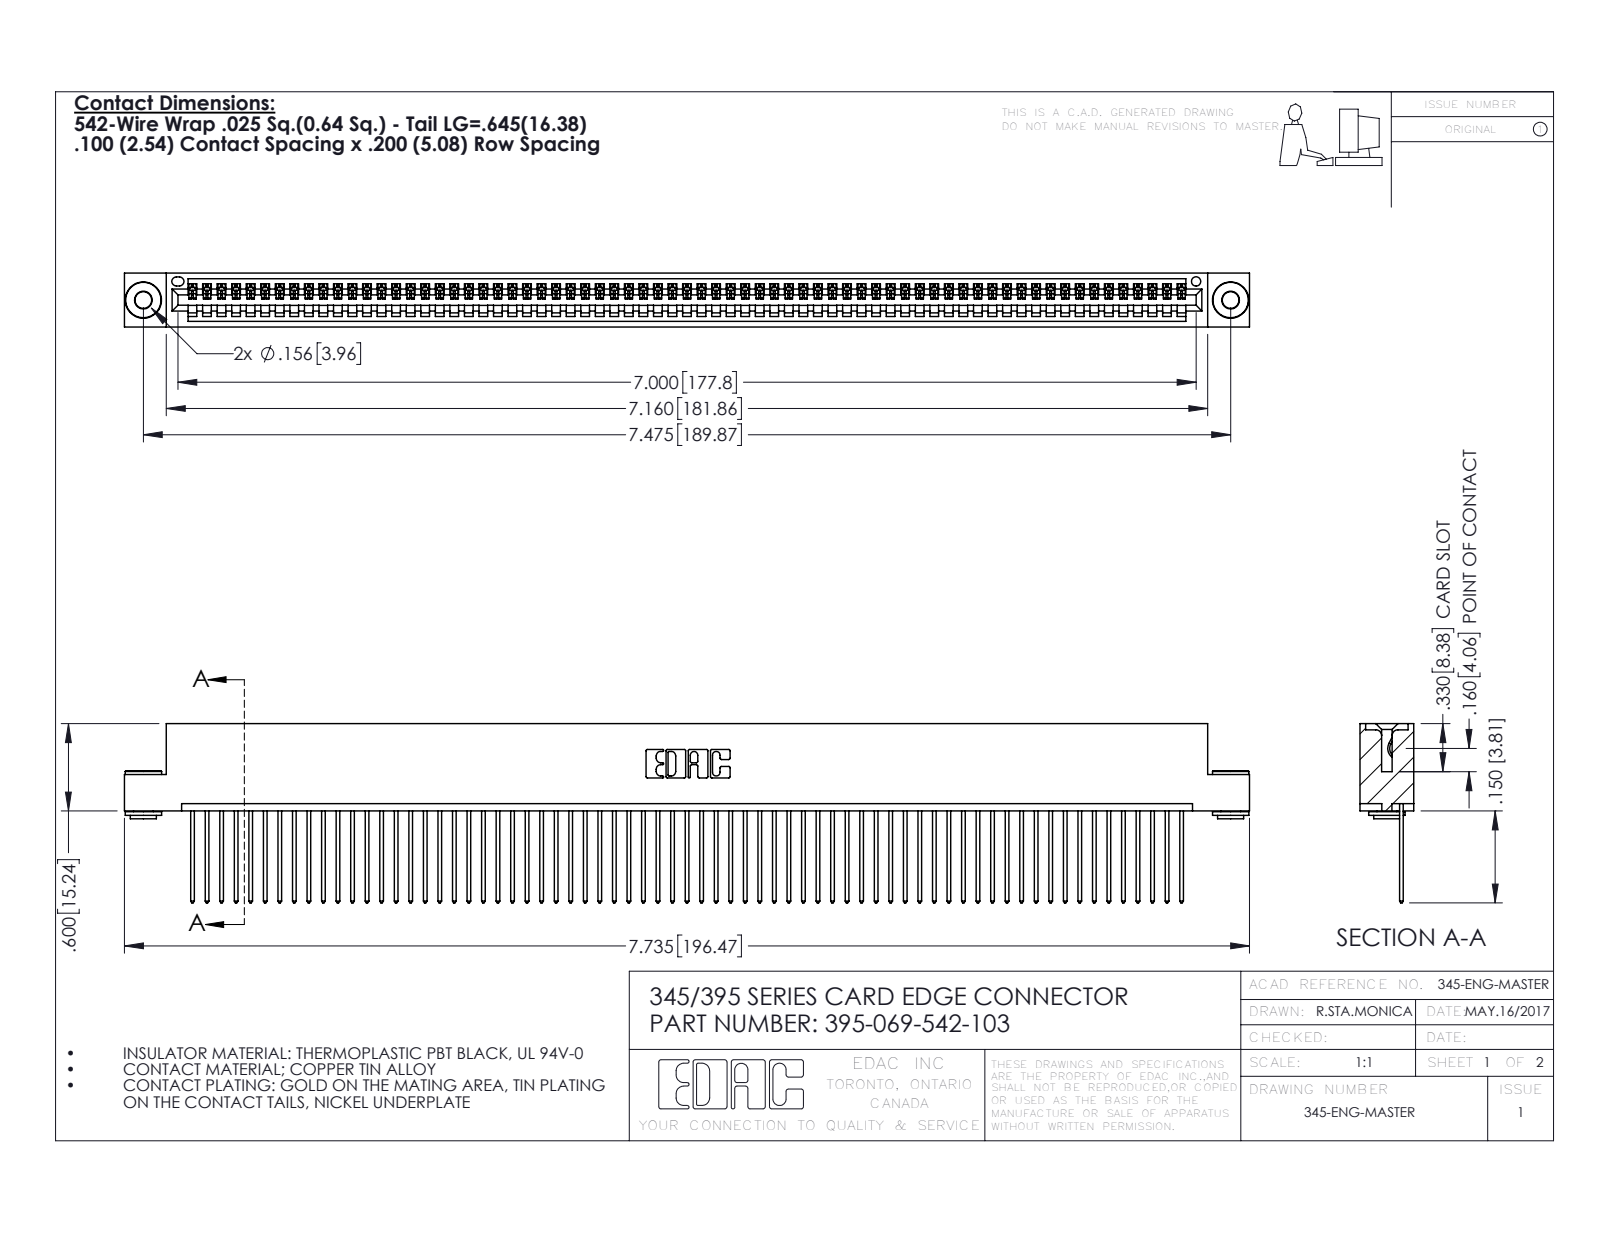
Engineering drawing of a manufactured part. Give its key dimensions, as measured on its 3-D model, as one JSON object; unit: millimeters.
{"part_name": "345 Part_Flush Mounting Lugs - 0.156 Dia-TH; 395-069-542-103; 345-250-002_345-250-002-102; 345-292-001_345-293-142", "step_written_by": "SolidWorks 2016 (CONFIG_CONTROL_DESIGN)", "units": "millimeters", "bodies": {"solids": 72, "faces": 4166, "planar": 2850, "cylindrical": 1308, "other": 8}, "overall_size": [196.5, 31.3, 9.4], "volume_mm3": 19060, "surface_area_mm2": 26880, "round_holes": [[2.9, 2], [4, 2], [1.6, 1]], "round_bosses_or_shafts": [[6.4, 2], [4.6, 2], [3.5, 2]], "partial_cylinders_radius": [[0.2, 138], [0.3, 138], [0.3, 22], [0.2, 6], [0.8, 6], [0.7, 3], [0.8, 2], [1, 2]], "face_to_face_distances": [1.8, 7.6, 0.6, 2.5, 6.9, 9.4, 5.1, 5.7, 3.8, 1.8], "hole_center_spacings": [6.9, 183.9, 189.9]}
